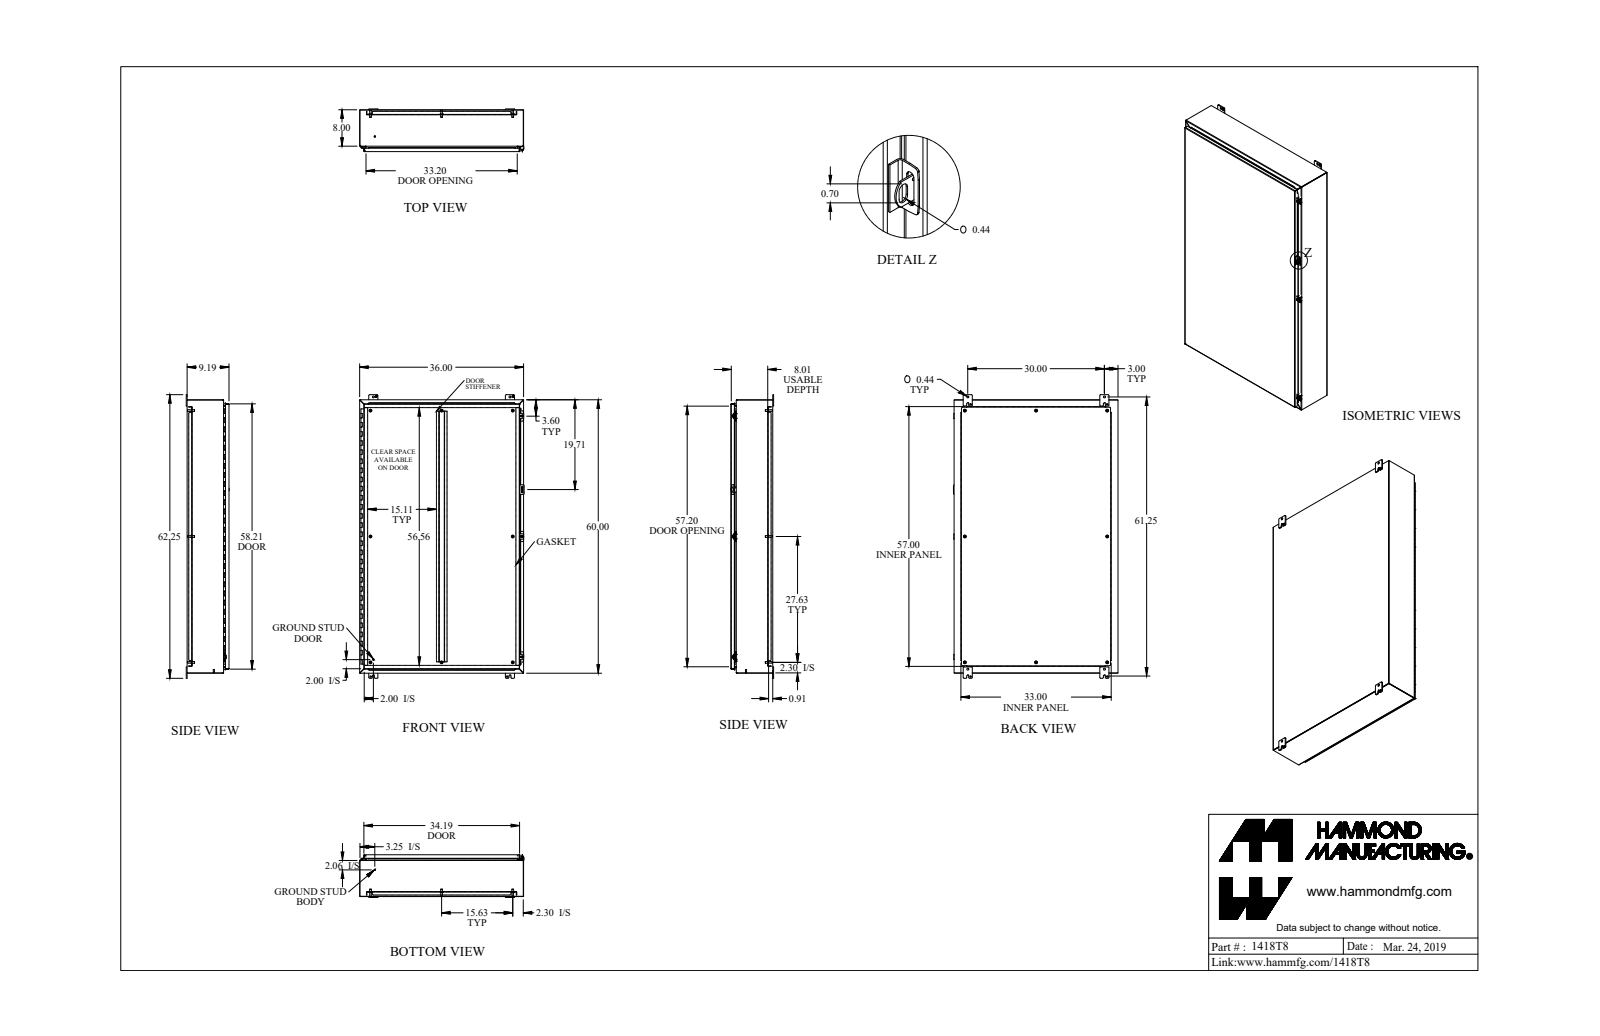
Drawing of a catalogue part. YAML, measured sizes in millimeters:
part_name: "1418T8_Default"
step_written_by: "SolidWorks 2019 (CONFIG_CONTROL_DESIGN)"
units: millimeters
bodies: {solids: 60, faces: 1900, planar: 1076, cylindrical: 701, other: 123}
overall_size: [1581.2, 917.6, 241.1]
volume: 11760000
surface_area: 11950000
round_holes:
  - {diameter: 12.7, count: 8}
  - {diameter: 7.8, count: 5}
  - {diameter: 11.3, count: 5}
  - {diameter: 8, count: 4}
  - {diameter: 11.1, count: 4}
  - {diameter: 5.4, count: 3}
  - {diameter: 6.7, count: 3}
  - {diameter: 9.5, count: 3}
  - {diameter: 3.2, count: 1}
  - {diameter: 4.7, count: 1}
  - {diameter: 5, count: 1}
  - {diameter: 6.4, count: 1}
round_bosses_or_shafts:
  - {diameter: 16.5, count: 8}
  - {diameter: 9.5, count: 8}
  - {diameter: 8.4, count: 8}
  - {diameter: 25.4, count: 5}
  - {diameter: 12.7, count: 3}
  - {diameter: 9.9, count: 3}
  - {diameter: 6.2, count: 3}
  - {diameter: 7.1, count: 2}
partial_cylinders:
  - {radius: 4.8, count: 34}
  - {radius: 6.4, count: 24}
  - {radius: 0.9, count: 22}
  - {radius: 2.7, count: 22}
  - {radius: 1.2, count: 19}
  - {radius: 3.6, count: 19}
  - {radius: 2.9, count: 16}
  - {radius: 1, count: 8}
face_to_face_distances: [1.8, 231.5, 229.6, 23.8, 233.3, 2.4, 25.6, 205.3, 203.4, 26.2]
hole_center_spacings: [806.1, 396.9, 701.7, 1458.4, 1612.3, 762, 793.8, 1059.4]
